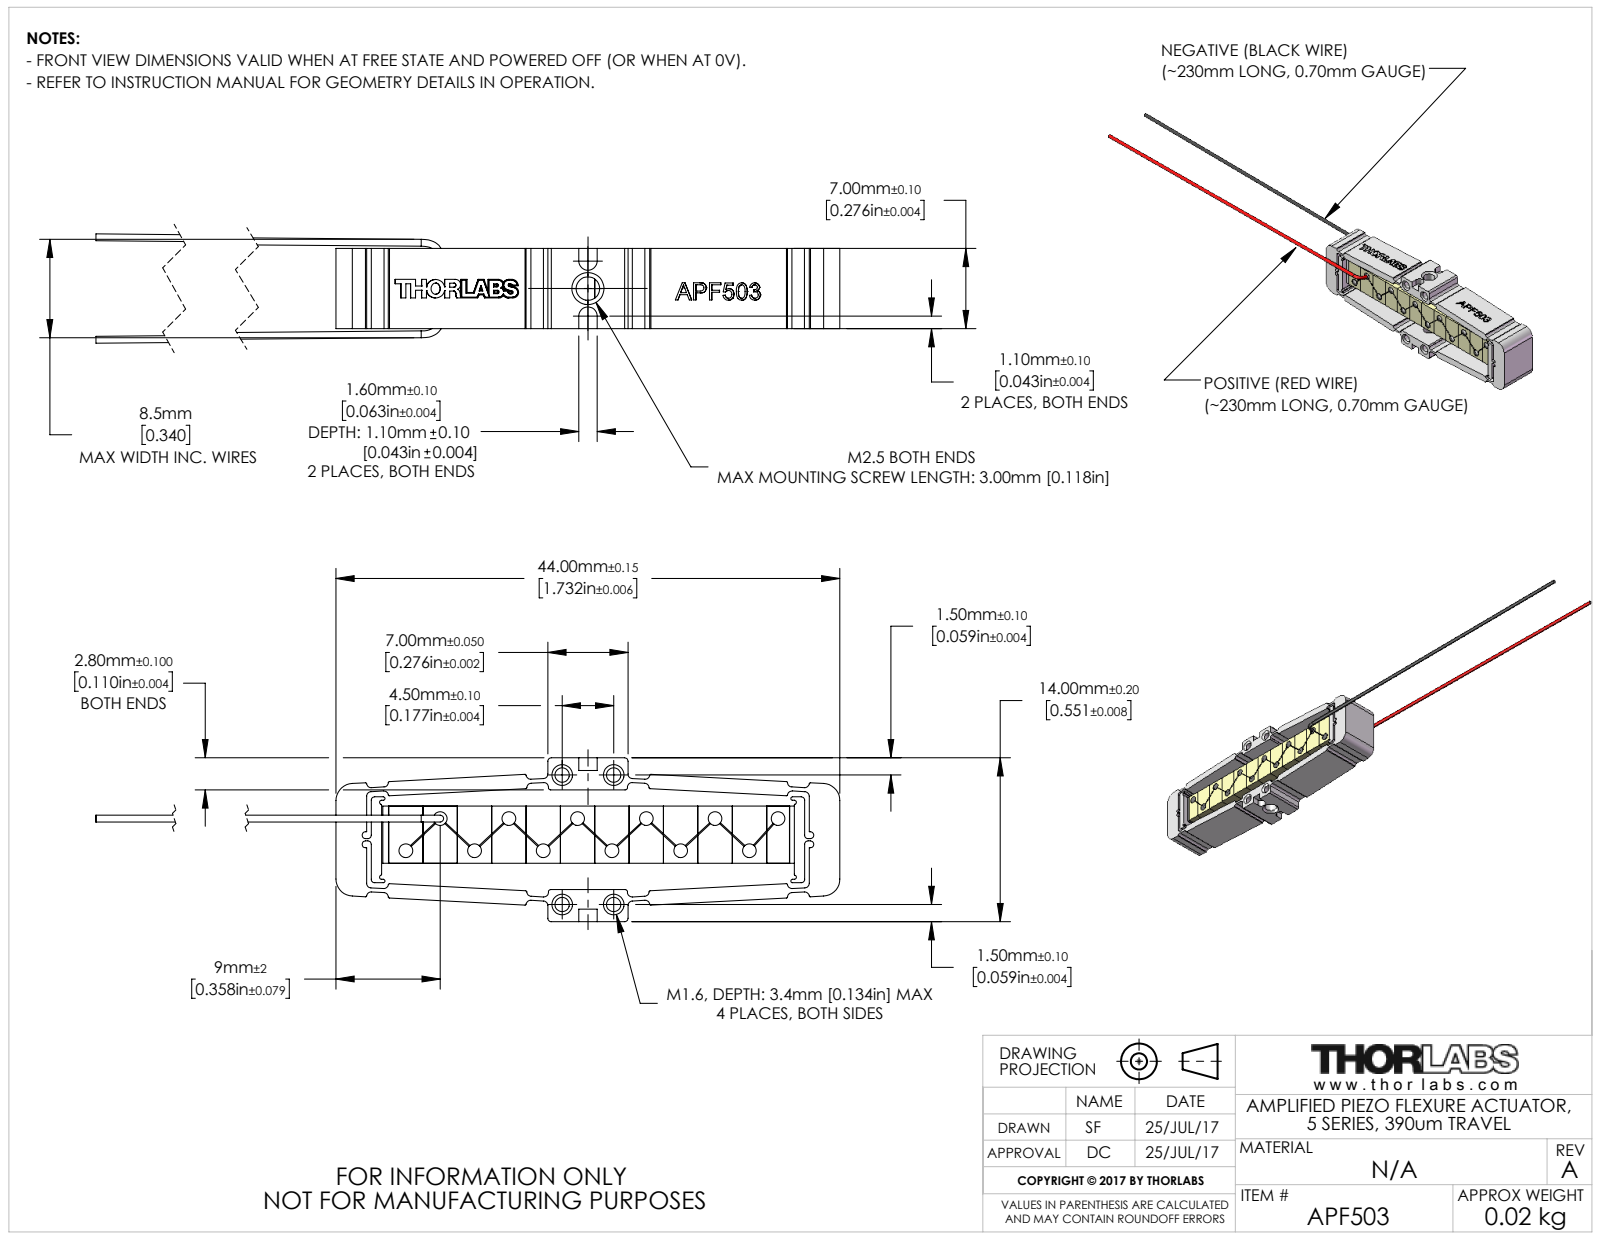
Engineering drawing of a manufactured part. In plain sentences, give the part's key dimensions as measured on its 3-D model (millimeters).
The part is named "APF503". Its 3-D file was written by "SolidWorks 2016 (CONFIG_CONTROL_DESIGN)". It is 0 solids with 618 faces: 269 planar, 234 cylindrical and 115 other. Overall it measures 96.55 by 14 by 9.53 millimeters. Round holes: 4 of diameter 1.25, 1 of diameter 1.62, 1 of diameter 2.05. Round bosses or shafts: 12 of diameter 1.2. Partial cylindrical surfaces (rounded edges, fillets, slot ends): 32 of radius 0.4, 24 of radius 0.1, 16 of radius 0.3, 4 of radius 0.15, 4 of radius 0.18, 4 of radius 0.2, 4 of radius 1.5, 2 of radius 0.44. The main face-to-face distances are 5, 10.34, 1.25, 6, 1, 7, 9.09, 11.59, 0.8, 0.45. The hole center spacings are 4.5, 10.99, 11.88.
